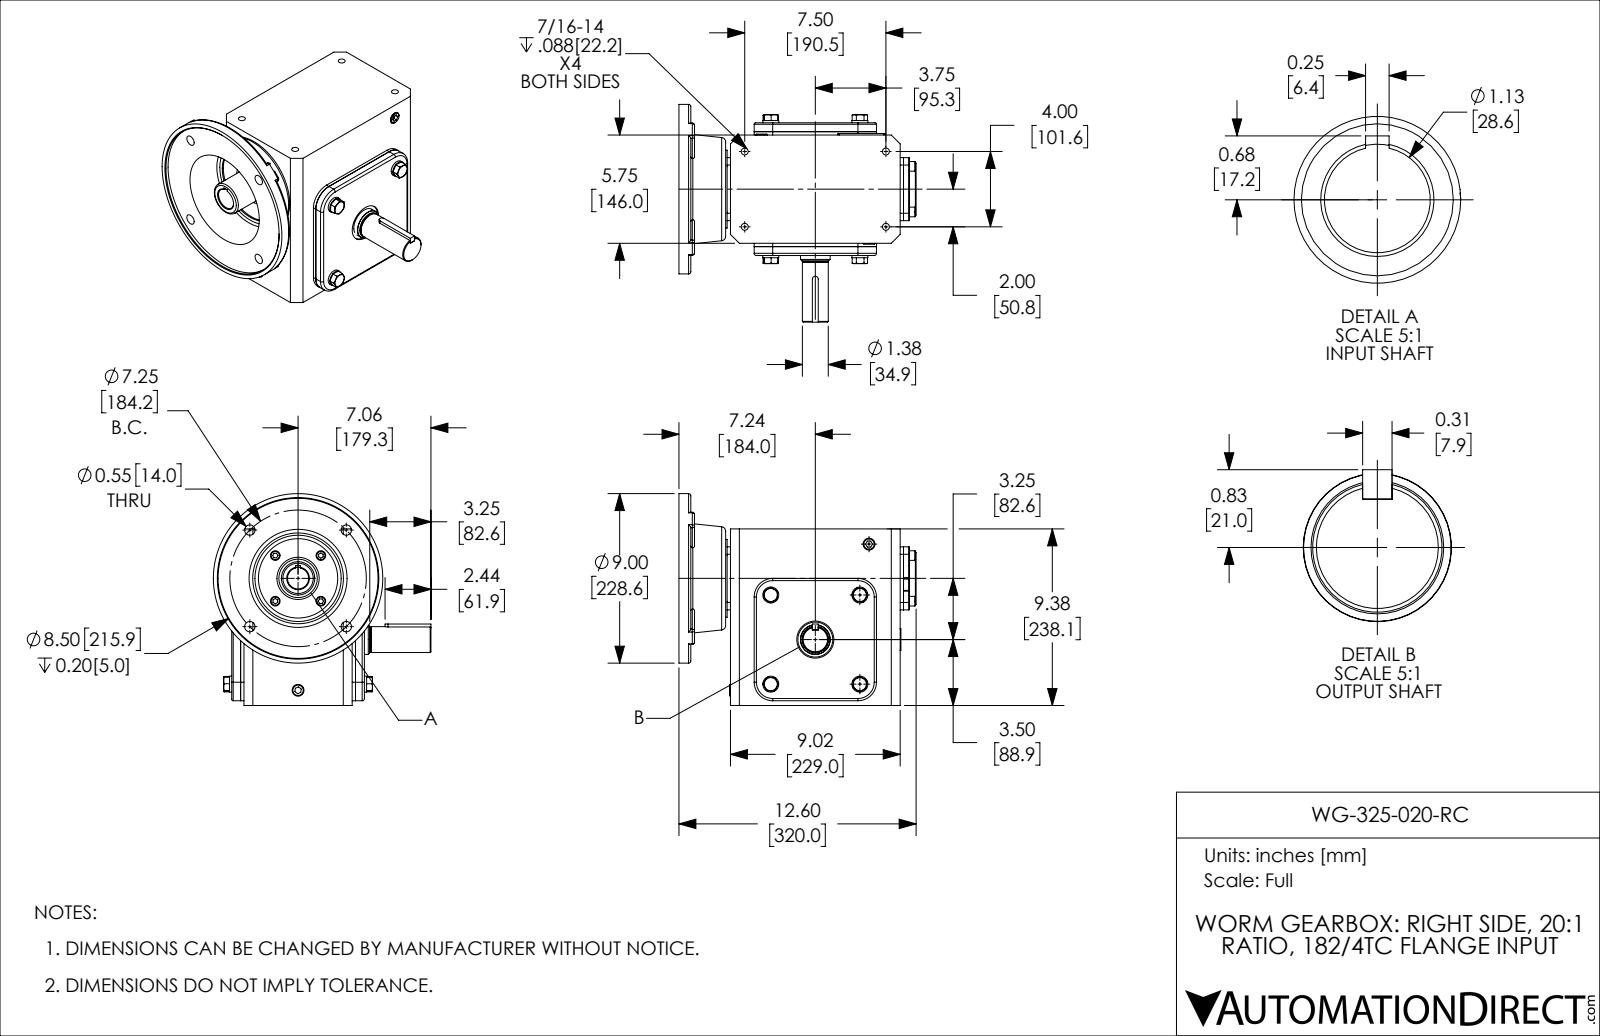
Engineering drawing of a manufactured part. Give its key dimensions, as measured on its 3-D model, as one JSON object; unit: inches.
{"part_name": "WG-325-020-RC", "step_written_by": "SolidWorks 2017 (AUTOMOTIVE_DESIGN)", "units": "inches", "bodies": {"solids": 40, "faces": 654, "planar": 336, "cylindrical": 196, "other": 122}, "overall_size": [12.598, 11.559, 11.25], "volume_in3": 529.7, "surface_area_in2": 1026, "round_holes": [[0.354, 4], [0.368, 4], [0.551, 4], [0.628, 3], [0.591, 1], [0.978, 1], [1.125, 1], [1.181, 1], [1.969, 1], [2.244, 1], [2.441, 1], [2.756, 1]], "round_bosses_or_shafts": [[0.846, 4], [0.512, 4], [9, 1], [4.134, 1], [2.835, 1], [1.772, 1], [1.575, 1], [1.375, 1]], "partial_cylinders_radius": [[0.118, 14], [0.079, 11], [0.394, 4], [0.906, 4], [0.984, 4], [0.02, 2], [0.039, 2], [0.156, 1]], "face_to_face_distances": [0.079, 0.177, 6.496, 0.394, 6.969, 0.472, 6.575, 6.398, 0.571, 0.65], "hole_center_spacings": [4.009, 1.713, 1.913, 2.422, 3.625, 5.127, 5.338, 2.372]}
